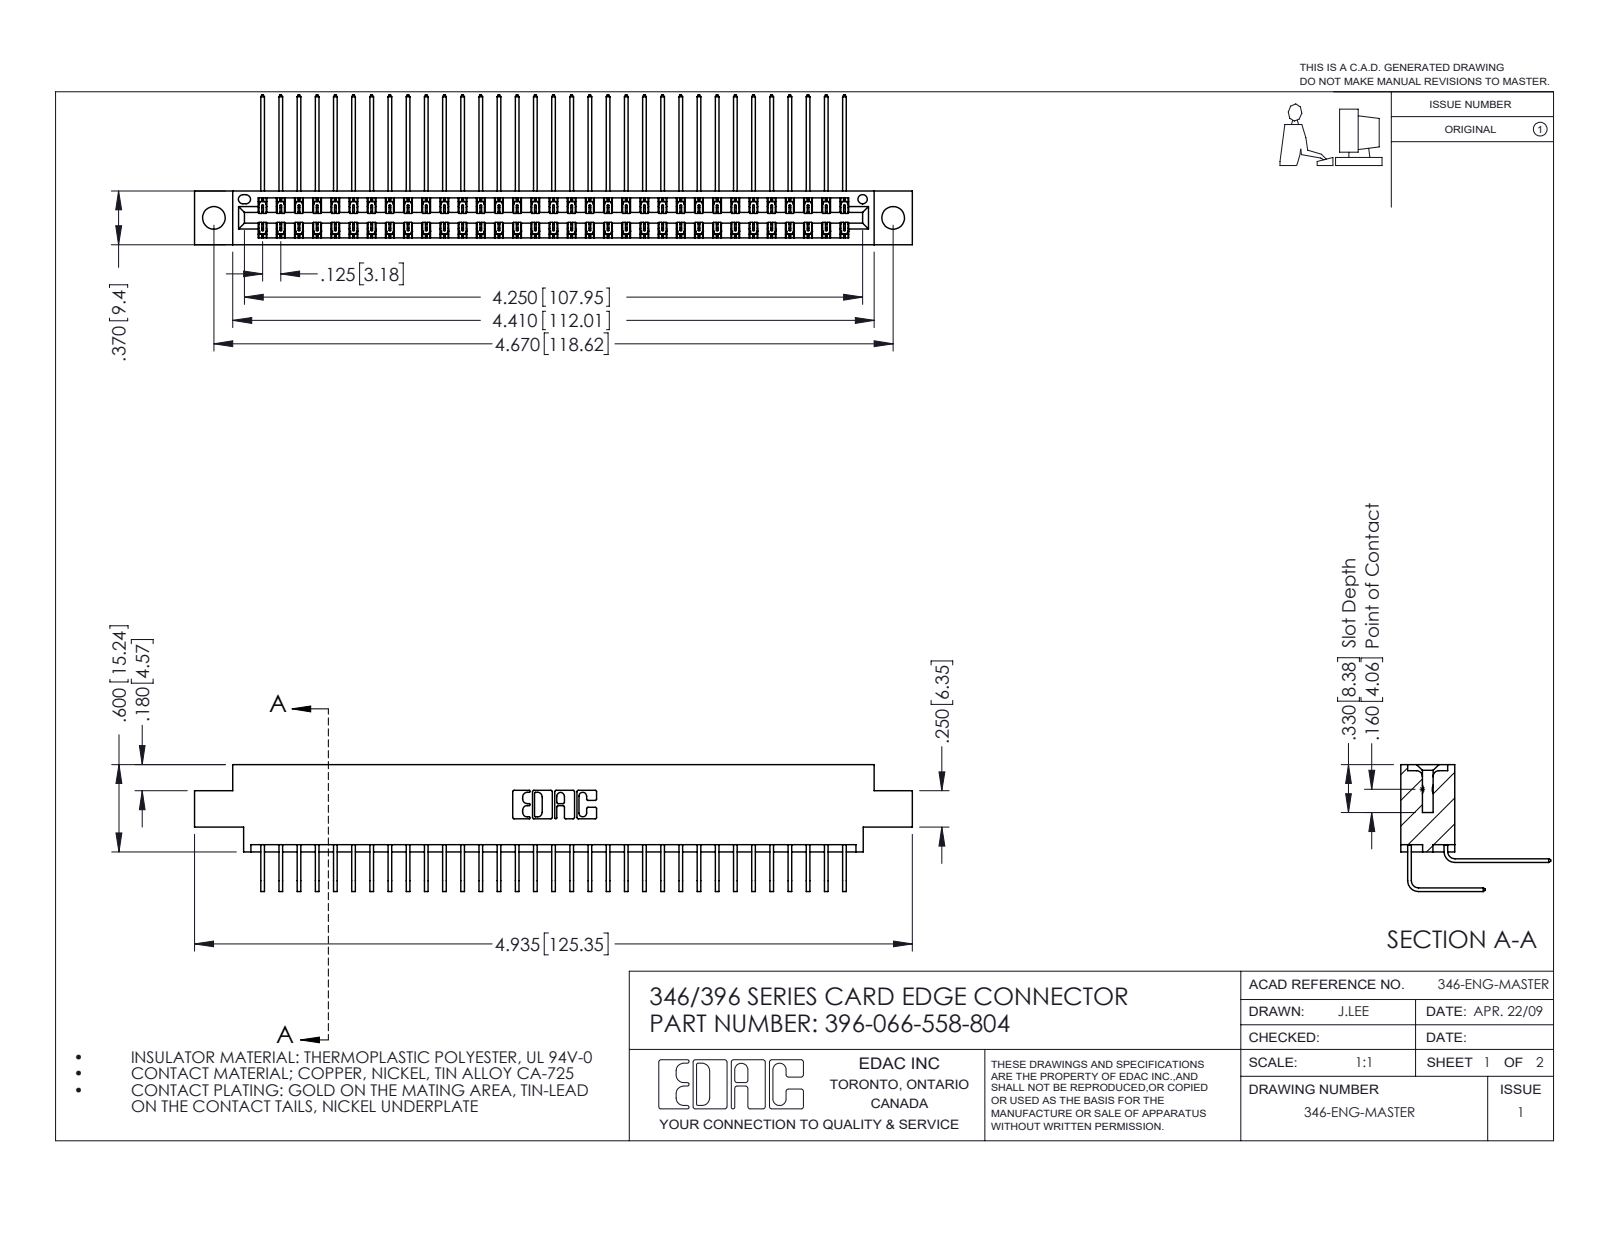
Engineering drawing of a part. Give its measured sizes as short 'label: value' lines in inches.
name: 346 Part_0.170 Offset - 0.156 Dia-TH; 396-066-558-804; 345-292-001_558 Tail - 2; 345-292-001_558 559 Tail - 1
written by: SolidWorks 2016 (CONFIG_CONTROL_DESIGN)
unit: in
bodies: 67 solids, 3690 faces (2522 planar, 1168 cylindrical, 0 other)
size: 4.935 × 1.03 × 0.873
volume: 0.75 in³; area: 28.79 in²
holes: 2× ⌀0.156, 1× ⌀0.064
rounds: 99× R0.006, 22× R0.01, 6× R0.007, 6× R0.031, 3× R0.026, 2× R0.014, 2× R0.022, 2× R0.024
face distances: 0.322, 0.048, 0.025, 0.37, 0.25, 0.298, 0.072, 0.275, 0.148, 0.222
hole spacings: 0.246, 4.462, 4.67
